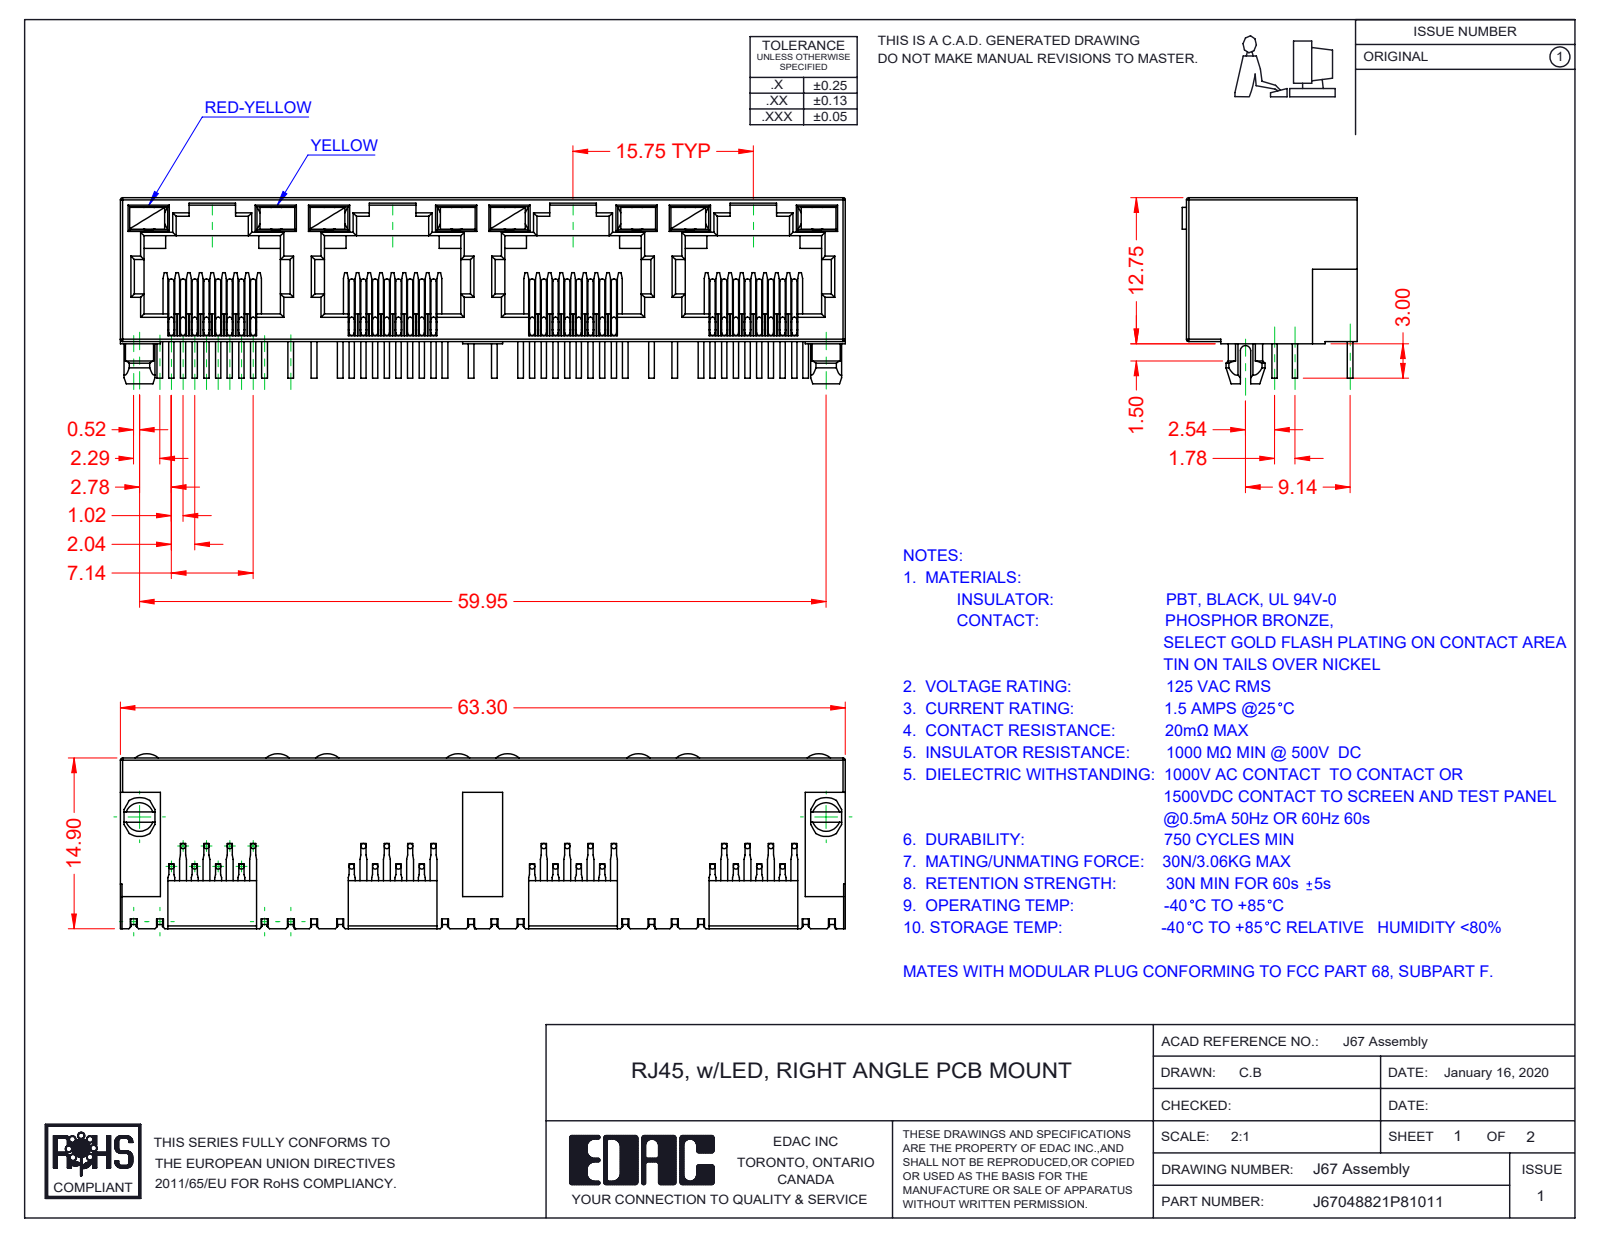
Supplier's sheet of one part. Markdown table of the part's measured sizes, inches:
| quantity | value |
| --- | --- |
| part name | J67048822P81011; 67 LED RH_1-Yellow; 67 LED LH_8-Red-Yellow; 67 Contacts (+1 more) |
| STEP written by | SolidWorks 2016 (CONFIG_CONTROL_DESIGN) |
| units | inches |
| bodies | 41 solids, 2473 faces (1781 planar, 484 cylindrical, 208 other) |
| overall size | 2.492 × 0.64 × 0.602 |
| volume | 0.315 in³ |
| surface area | 17.94 in² |
| round bosses / shafts (diameter × count) | 0.018 × 96 |
| partial cylindrical surfaces (radius × count) | 0.008 × 66, 0.012 × 29, 0.018 × 9, 0.061 × 8, 0.059 × 2, 0.067 × 2, 0.014 × 1, 0.039 × 1 |
| main face-to-face distances | 0.02, 0.494, 0.074, 0.035, 0.394, 0.62, 0.039, 0.055, 0.433, 0.468 |
